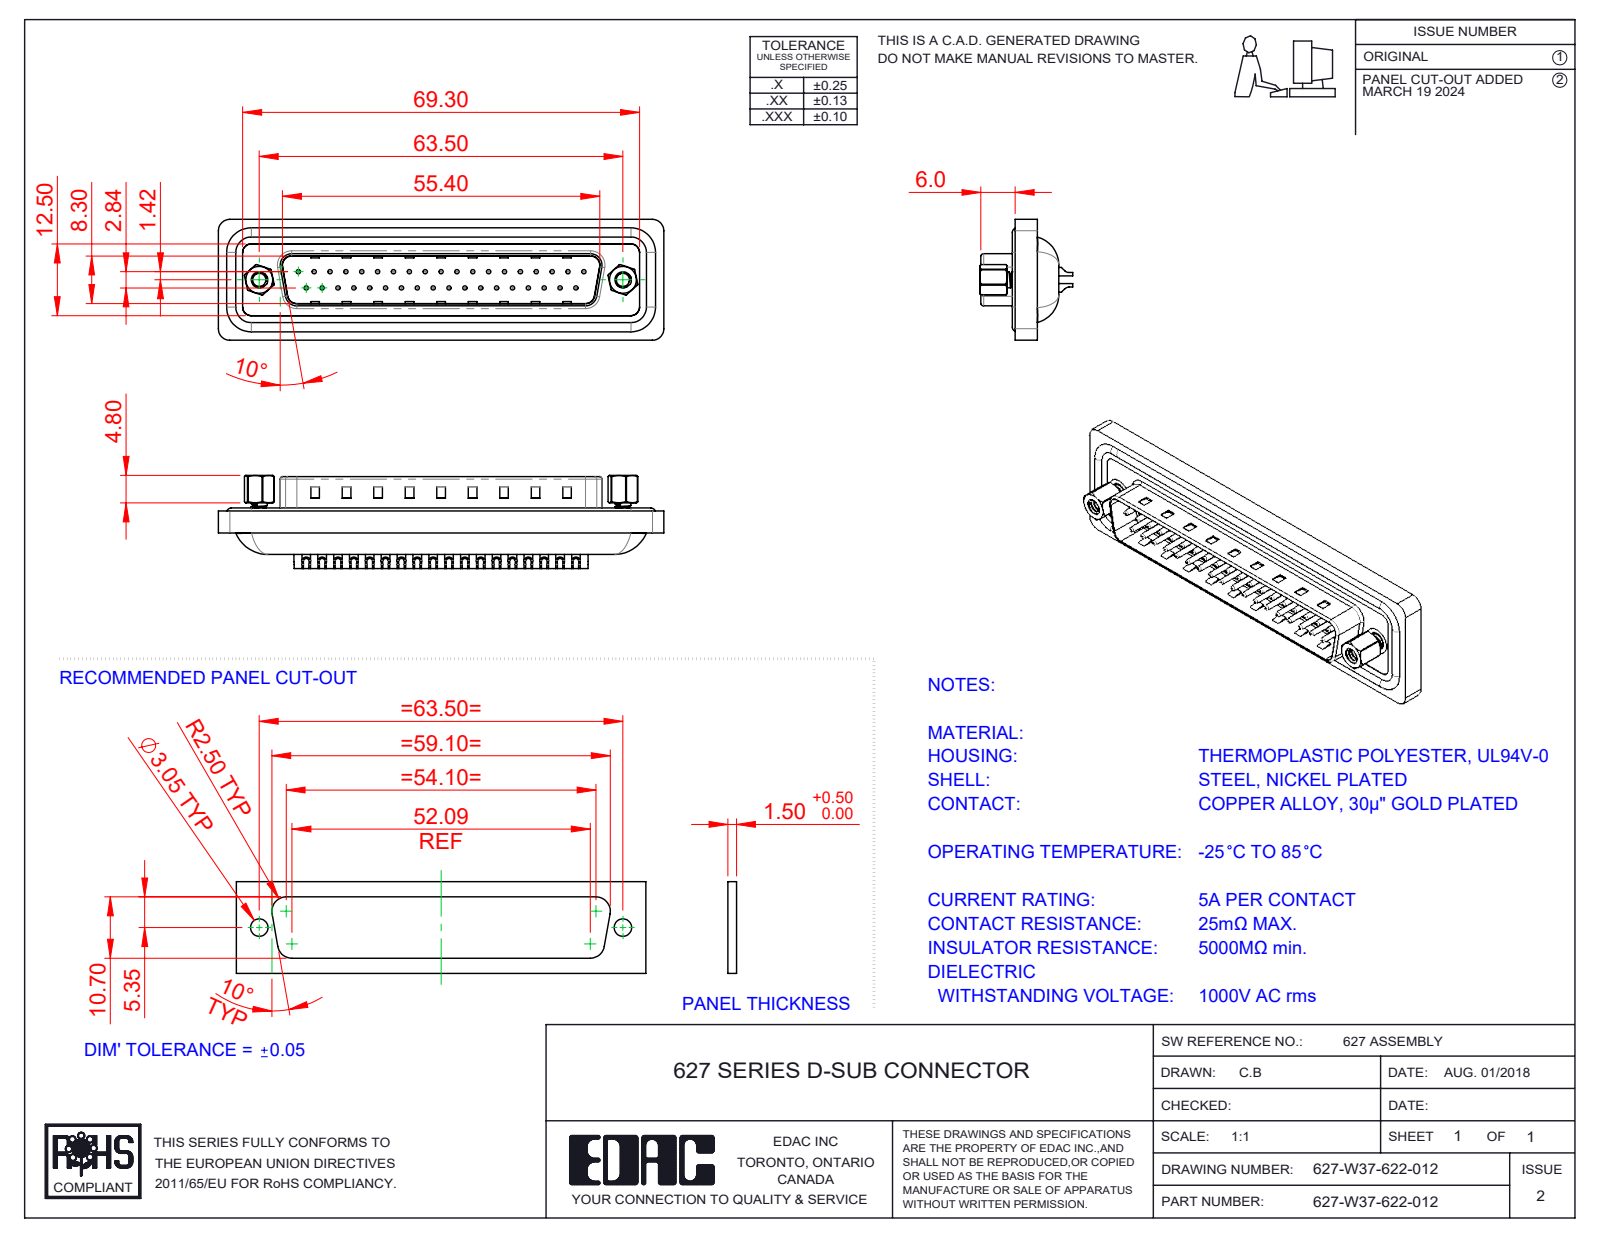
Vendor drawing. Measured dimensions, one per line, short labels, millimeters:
name: 627W Shell Front_37 Contacts; 627W 4-40 Threaded Rivet; 627W Housing_37 Contacts; 627-W37-622-012 (+4 more)
written by: SolidWorks 2023 (CONFIG_CONTROL_DESIGN)
unit: mm
bodies: 45 solids, 1999 faces (570 planar, 890 cylindrical, 539 other)
size: 77.8 × 21.1 × 16.25
volume: 9 568 mm³; area: 14 622 mm²
holes: 37× ⌀0.75, 37× ⌀1, 37× ⌀1.5, 37× ⌀1.6, 37× ⌀2, 2× ⌀2.26, 2× ⌀2.29, 2× ⌀4, 2× ⌀4.8, 2× ⌀5
bosses: 9× ⌀1.5, 4× ⌀1.6, 2× ⌀4.9, 2× ⌀2.79
rounds: 16× R2, 14× R1.5, 8× R0.5, 6× R2.7, 4× R0.9, 4× R1.6, 4× R4.3, 2× R0.4
face distances: 0.75, 0.4, 4.1, 1.1, 2.75, 4.6, 3.75, 5.65, 15.45, 14.7
hole spacings: 3.16, 2.77, 5.54, 8.31, 5.04, 10.1, 11.08, 12.78
